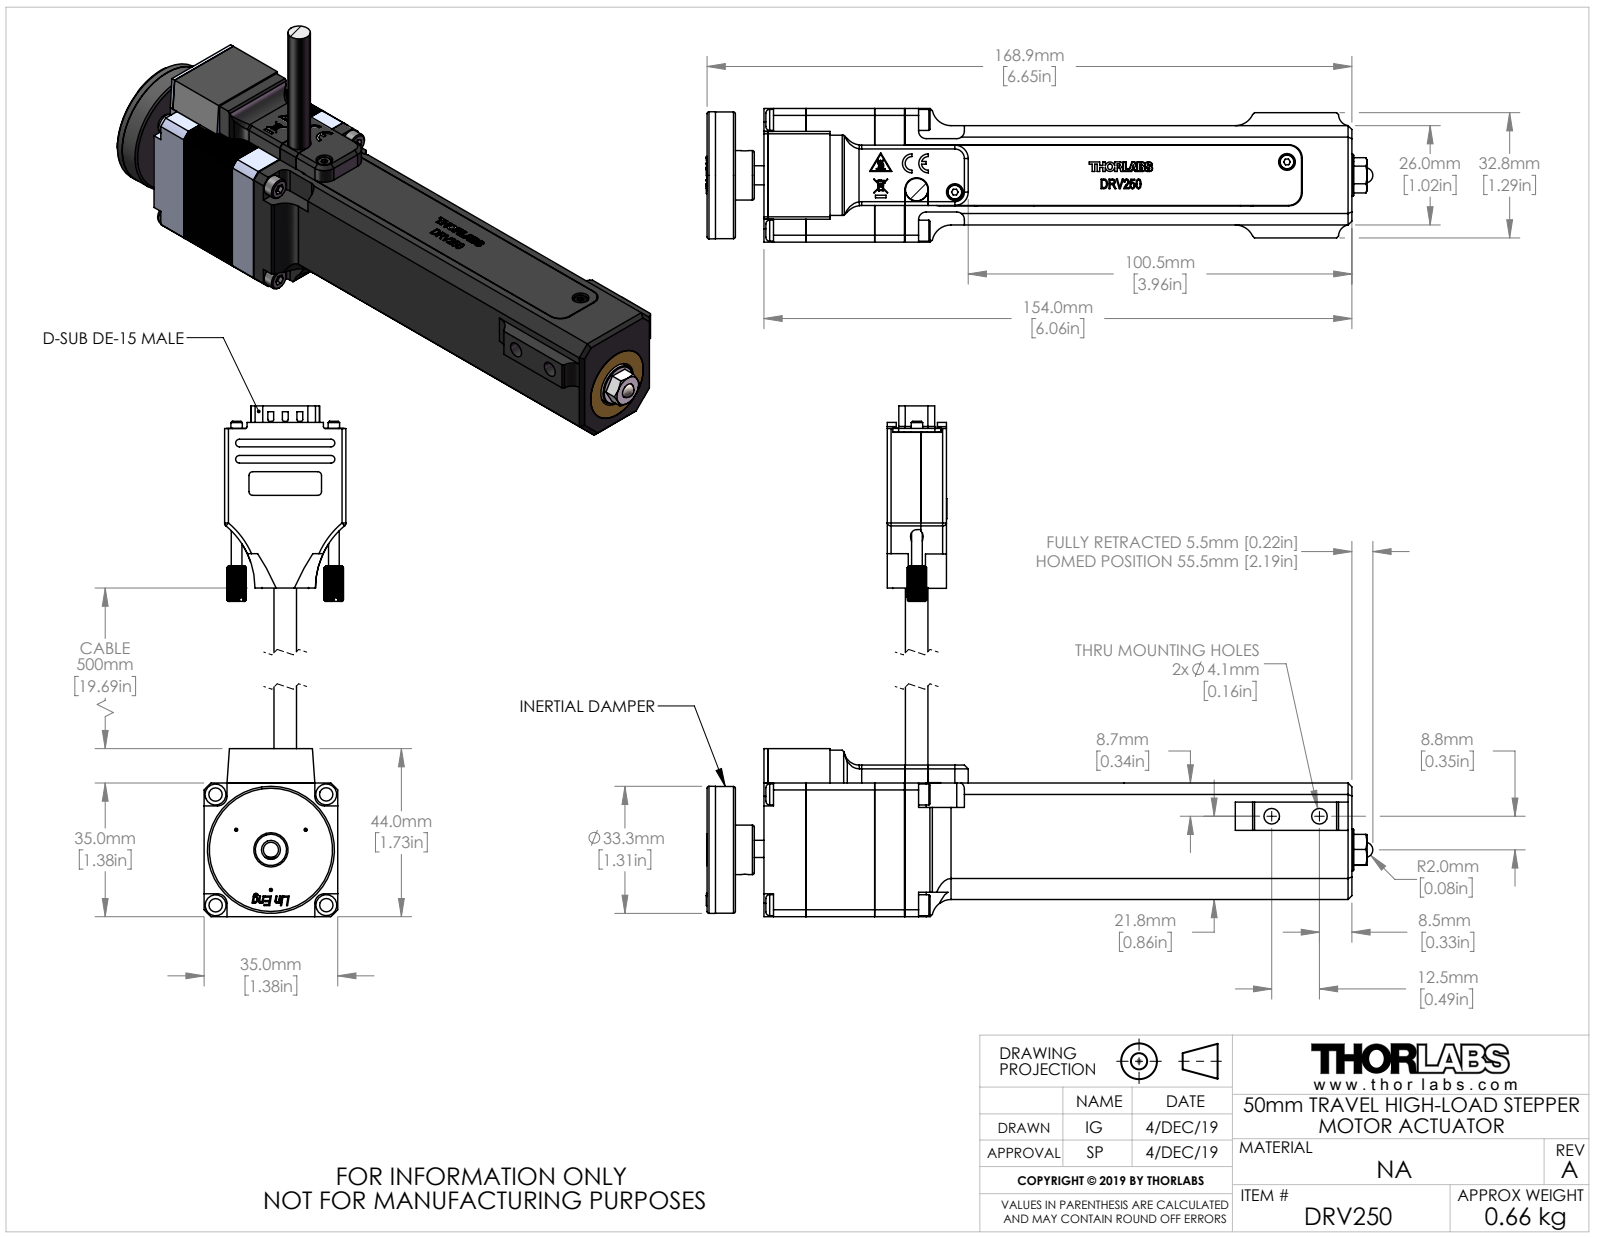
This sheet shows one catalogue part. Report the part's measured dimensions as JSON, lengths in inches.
{"part_name": "DRV250 - 50mm Trapezoidal Stepper Motor Drive", "step_written_by": "SolidWorks 2019 (AUTOMOTIVE_DESIGN)", "units": "inches", "bodies": {"solids": 22, "faces": 1014, "planar": 584, "cylindrical": 0, "other": 430}, "overall_size": [6.874, 3.01, 1.378], "volume_in3": 8.414, "surface_area_in2": 97.19, "face_to_face_distances": [0.177, 1.201, 1.024, 1.378, 1.142, 0.709, 0.059, 0.315, 0.236, 0.197]}
